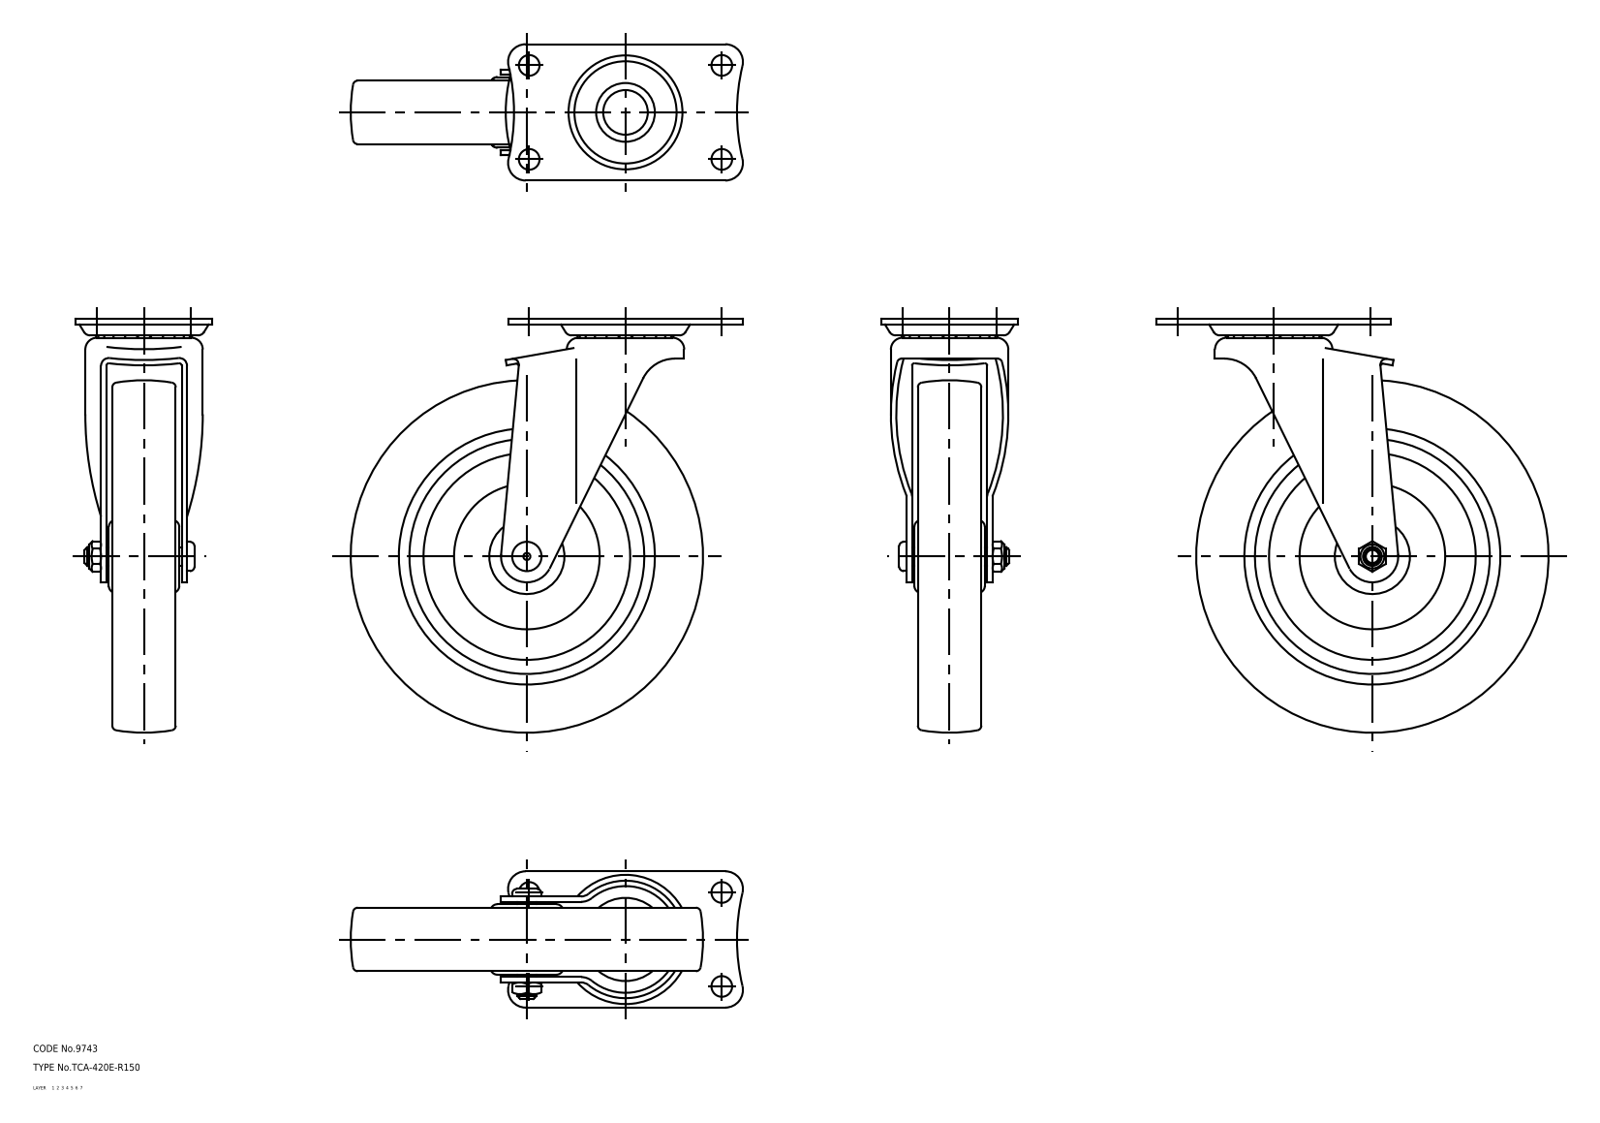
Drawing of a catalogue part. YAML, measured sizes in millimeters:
part_name: "wheel; mounting plate; main shaft; axle (+1 more)"
step_written_by: "CADfix (AUTOMOTIVE_DESIGN)"
units: millimeters
bodies: {solids: 5, faces: 247, planar: 0, cylindrical: 0, other: 247}
overall_size: [176, 167, 58]
volume: 512115
surface_area: 89906
